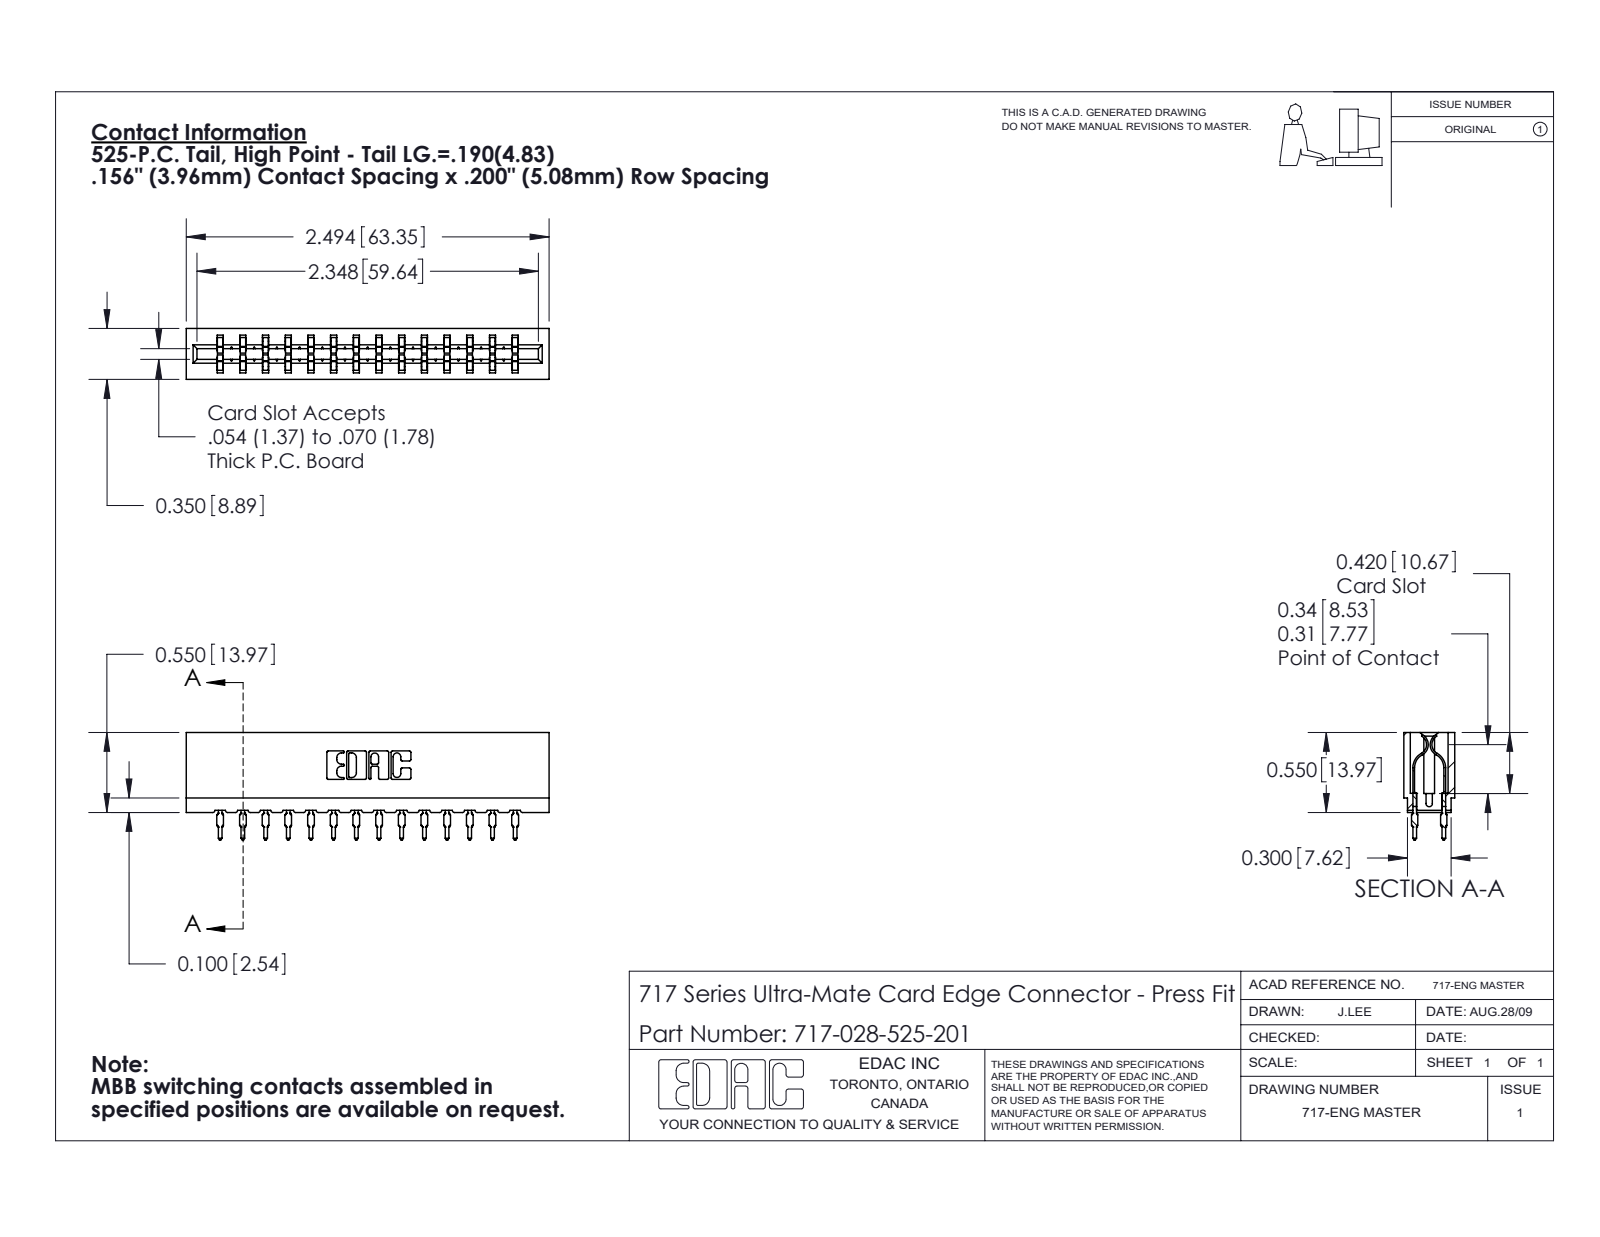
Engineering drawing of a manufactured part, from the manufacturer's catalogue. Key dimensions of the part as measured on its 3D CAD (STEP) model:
Part name (STEP PRODUCT): 717 Part_Insulator Option - 06; 717-028-525-201; 745-292-001_525
STEP written by: SolidWorks 2020 (CONFIG_CONTROL_DESIGN)
Units: inches
Bodies: 29 solids, 2614 faces (1356 planar, 530 cylindrical, 728 other)
Overall size (bounding box): 2.494 × 0.739 × 0.35
Volume: 0.342 in³ · Surface area: 12.64 in²
Partial cylindrical surfaces — rounded edges, fillets, slot ends (radius × count): R0.021 ×56, R0.015 ×28, R0.01 ×22, R0.005 ×8, R0.011 ×8, R0.007 ×6, R0.031 ×6, R0.026 ×3
Main face-to-face distances: 0.212, 0.138, 0.156, 0.35, 0.624, 0.198, 0.312, 0.468, 0.063, 0.287
